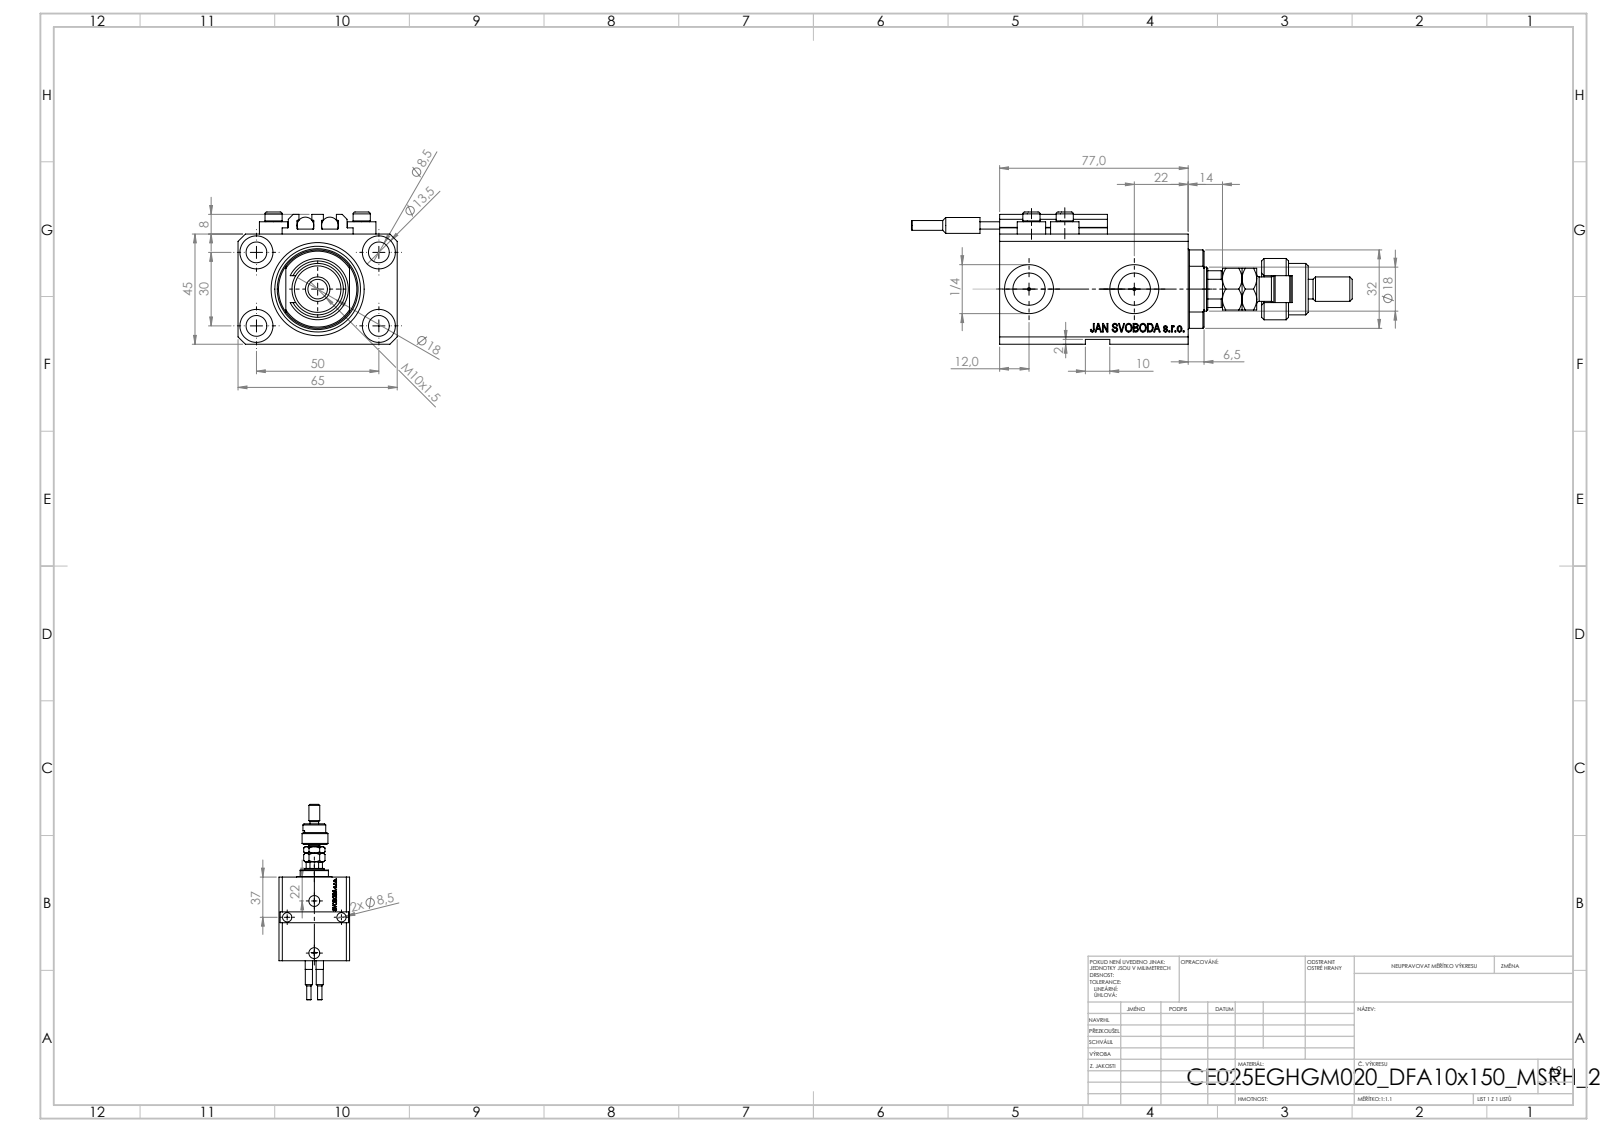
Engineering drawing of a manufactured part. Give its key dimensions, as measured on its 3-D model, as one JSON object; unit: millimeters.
{"part_name": "ALLEN BOLT V250CE; V250CE_VC_E; MFA; V250CE_C_VCP (+3 more)", "step_written_by": "SolidWorks 2019 (CONFIG_CONTROL_DESIGN)", "units": "millimeters", "bodies": {"solids": 12, "faces": 1204, "planar": 571, "cylindrical": 151, "other": 482}, "overall_size": [180, 65, 54], "volume_mm3": 215142, "surface_area_mm2": 67381, "round_holes": [[8.5, 7], [1.25, 4], [4, 4], [13.5, 4], [10, 2], [13.16, 2], [20, 2], [18, 1], [38, 1]], "round_bosses_or_shafts": [[11.6, 4], [7, 4], [6.8, 2], [6.5, 2], [4, 2], [25, 1], [21, 1], [16, 1]], "partial_cylinders_radius": [[0.2, 10], [5.5, 1], [8.5, 1], [8.75, 1], [16, 1]], "face_to_face_distances": [45, 14, 65, 63, 2, 77, 3, 5, 47, 6.9], "hole_center_spacings": [29.15, 50, 13.6, 15.12, 18.81, 18.97, 26.22, 26.61]}
